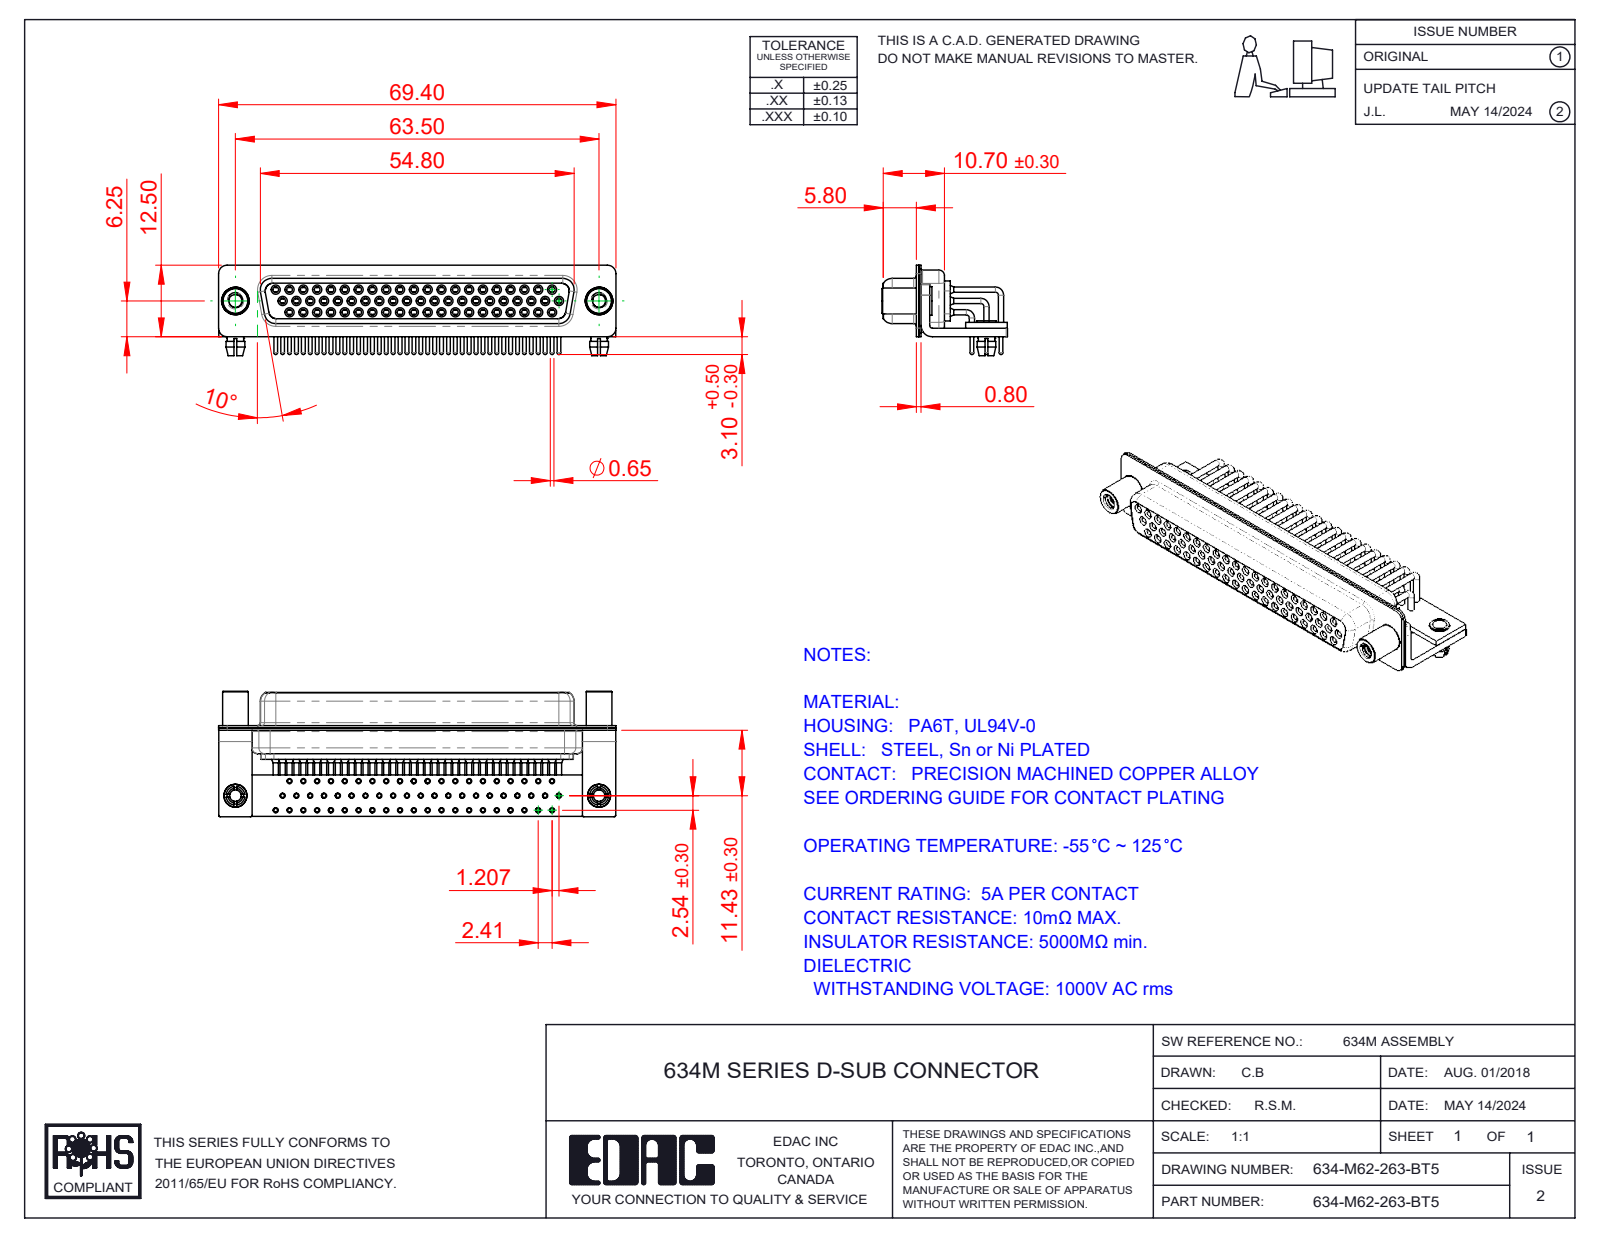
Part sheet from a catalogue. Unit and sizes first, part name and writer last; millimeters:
Units: millimetres
Overall size (bounding box): 69.4 × 21.9 × 15.8
Round holes (diameter × count): ⌀2 ×64, ⌀0.9 ×62, ⌀1 ×62, ⌀1.1 ×62, ⌀1.7 ×62, ⌀1.8 ×62, ⌀2.26 ×2, ⌀2.5 ×2, ⌀3.2 ×2, ⌀4 ×2, ⌀4.8 ×2
Round bosses / shafts (diameter × count): ⌀0.9 ×118, ⌀1.6 ×62, ⌀1.5 ×62, ⌀0.65 ×62, ⌀2 ×56, ⌀5 ×2, ⌀4.9 ×2, ⌀4.5 ×2
Partial cylindrical surfaces — rounded edges, fillets, slot ends (radius × count): R0.25 ×16, R1.5 ×16, R2 ×13, R1.35 ×8, R1.6 ×8, R0.5 ×5, R0.6 ×4, R0.65 ×4
Main face-to-face distances: 0.4, 2.3, 1.9, 1, 8.5, 1.45, 8.95, 0.85, 0.8, 9.35
Hole centre spacings: 7.24, 2.41, 9.65, 4.83, 14.48, 16.89, 2.81, 2.32
Volume: 6 304 mm³ · Surface area: 20 284 mm²
Bodies: 72 solids, 3881 faces (1073 planar, 1783 cylindrical, 1025 other)
Part name (STEP PRODUCT): 634-M62-263-BT5; 634M Contact Row 1; 634M Shell Rear_62 Contacts; 634M Shell Front_62 Contacts (+7 more)
STEP written by: SolidWorks 2016 (CONFIG_CONTROL_DESIGN)
